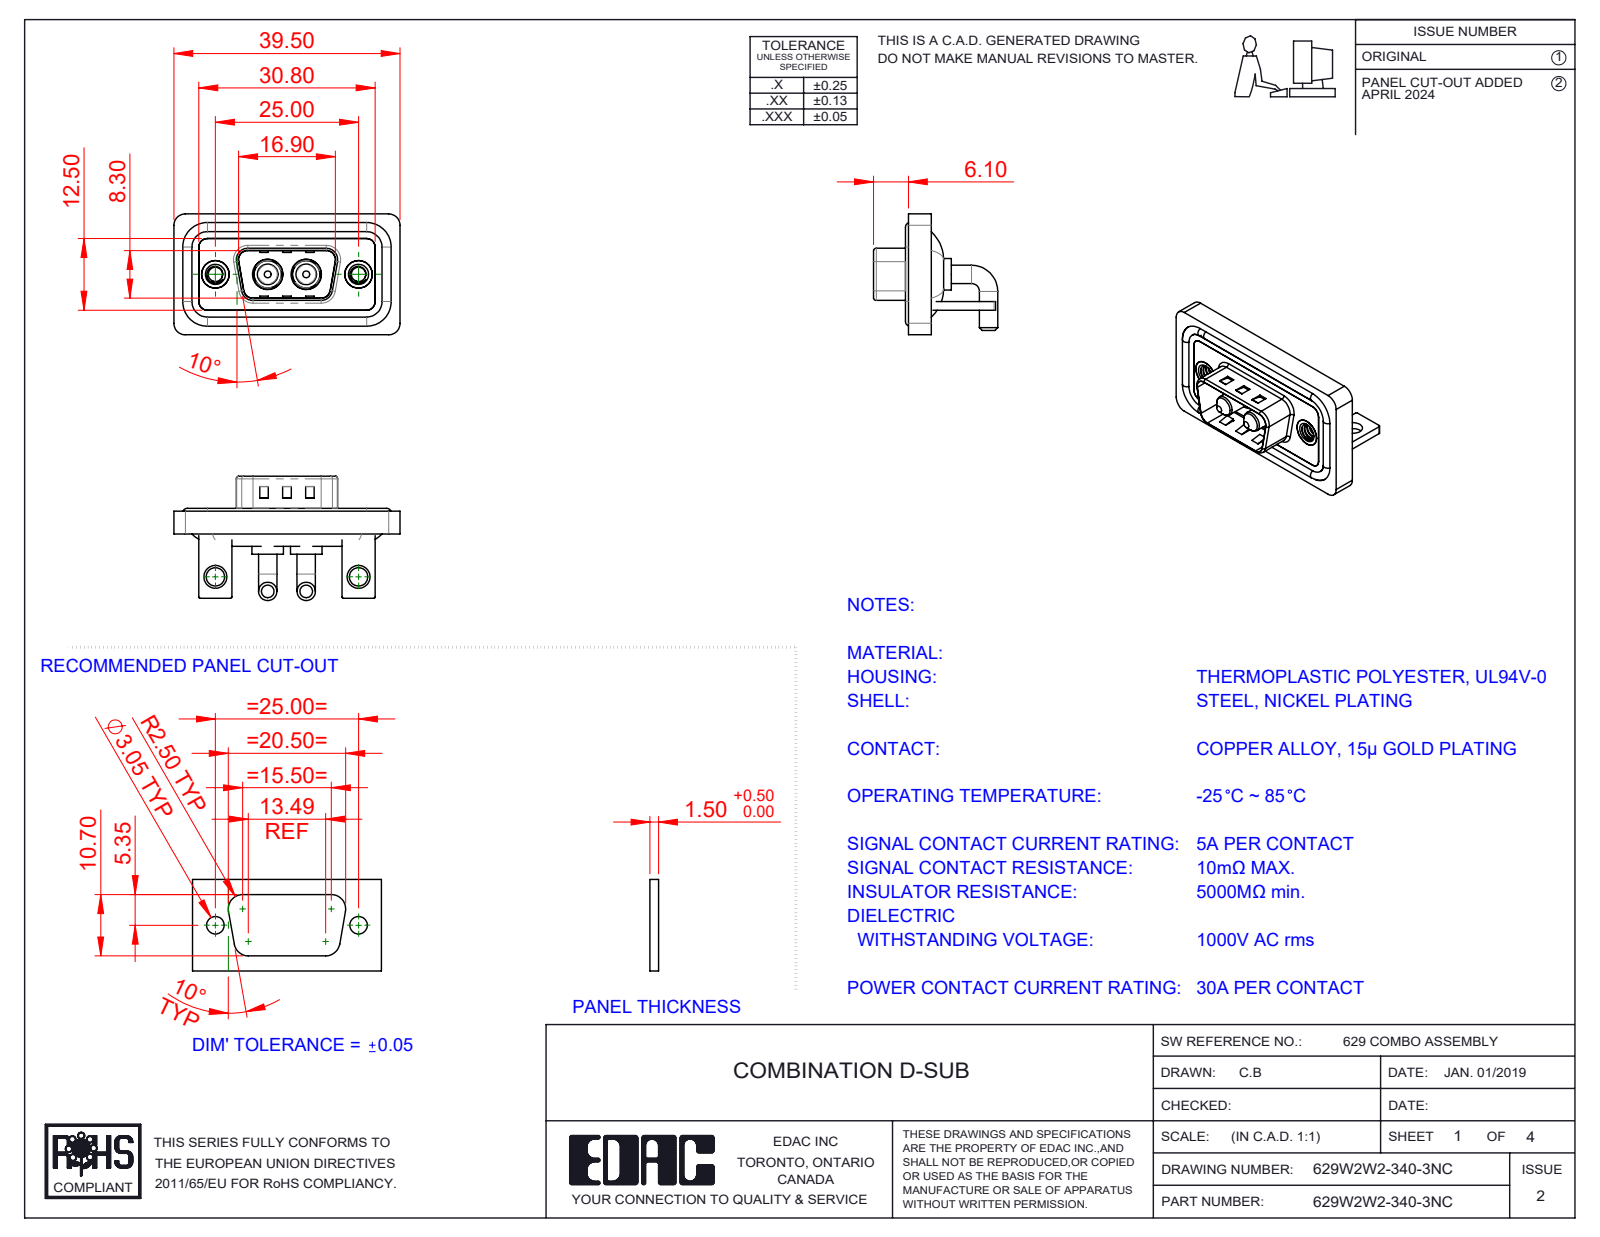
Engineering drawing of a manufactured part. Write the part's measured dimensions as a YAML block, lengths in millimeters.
part_name: "629Combo Waterproof Housing_09 Contacts; 629Combo Stabilizer Bracket; 629W2W2-340-3NC; 629Combo Shell Rear_09 Contacts (+4 more)"
step_written_by: "SolidWorks 2023 (CONFIG_CONTROL_DESIGN)"
units: millimeters
bodies: {solids: 13, faces: 535, planar: 185, cylindrical: 240, other: 110}
overall_size: [39.5, 21.7, 21.1]
volume: 4912
surface_area: 7792
round_holes:
  - {diameter: 2.5, count: 2}
  - {diameter: 3.2, count: 2}
  - {diameter: 4, count: 2}
  - {diameter: 4.8, count: 2}
  - {diameter: 4.85, count: 2}
  - {diameter: 5, count: 2}
  - {diameter: 5.3, count: 2}
round_bosses_or_shafts:
  - {diameter: 3.2, count: 4}
  - {diameter: 1.6, count: 4}
  - {diameter: 5.5, count: 2}
  - {diameter: 5.2, count: 2}
  - {diameter: 4.9, count: 2}
  - {diameter: 4.75, count: 2}
  - {diameter: 3.75, count: 2}
  - {diameter: 3.6, count: 2}
partial_cylinders:
  - {radius: 2, count: 19}
  - {radius: 1.5, count: 18}
  - {radius: 0.25, count: 16}
  - {radius: 0.5, count: 9}
  - {radius: 1.6, count: 8}
  - {radius: 0.6, count: 4}
  - {radius: 0.65, count: 4}
  - {radius: 0.9, count: 4}
face_to_face_distances: [0.4, 1.5, 2.9, 0.8, 1.1, 1.2, 2.1, 1.6, 3.7, 2.5]
hole_center_spacings: [9.14, 15.86, 25, 6.72]
